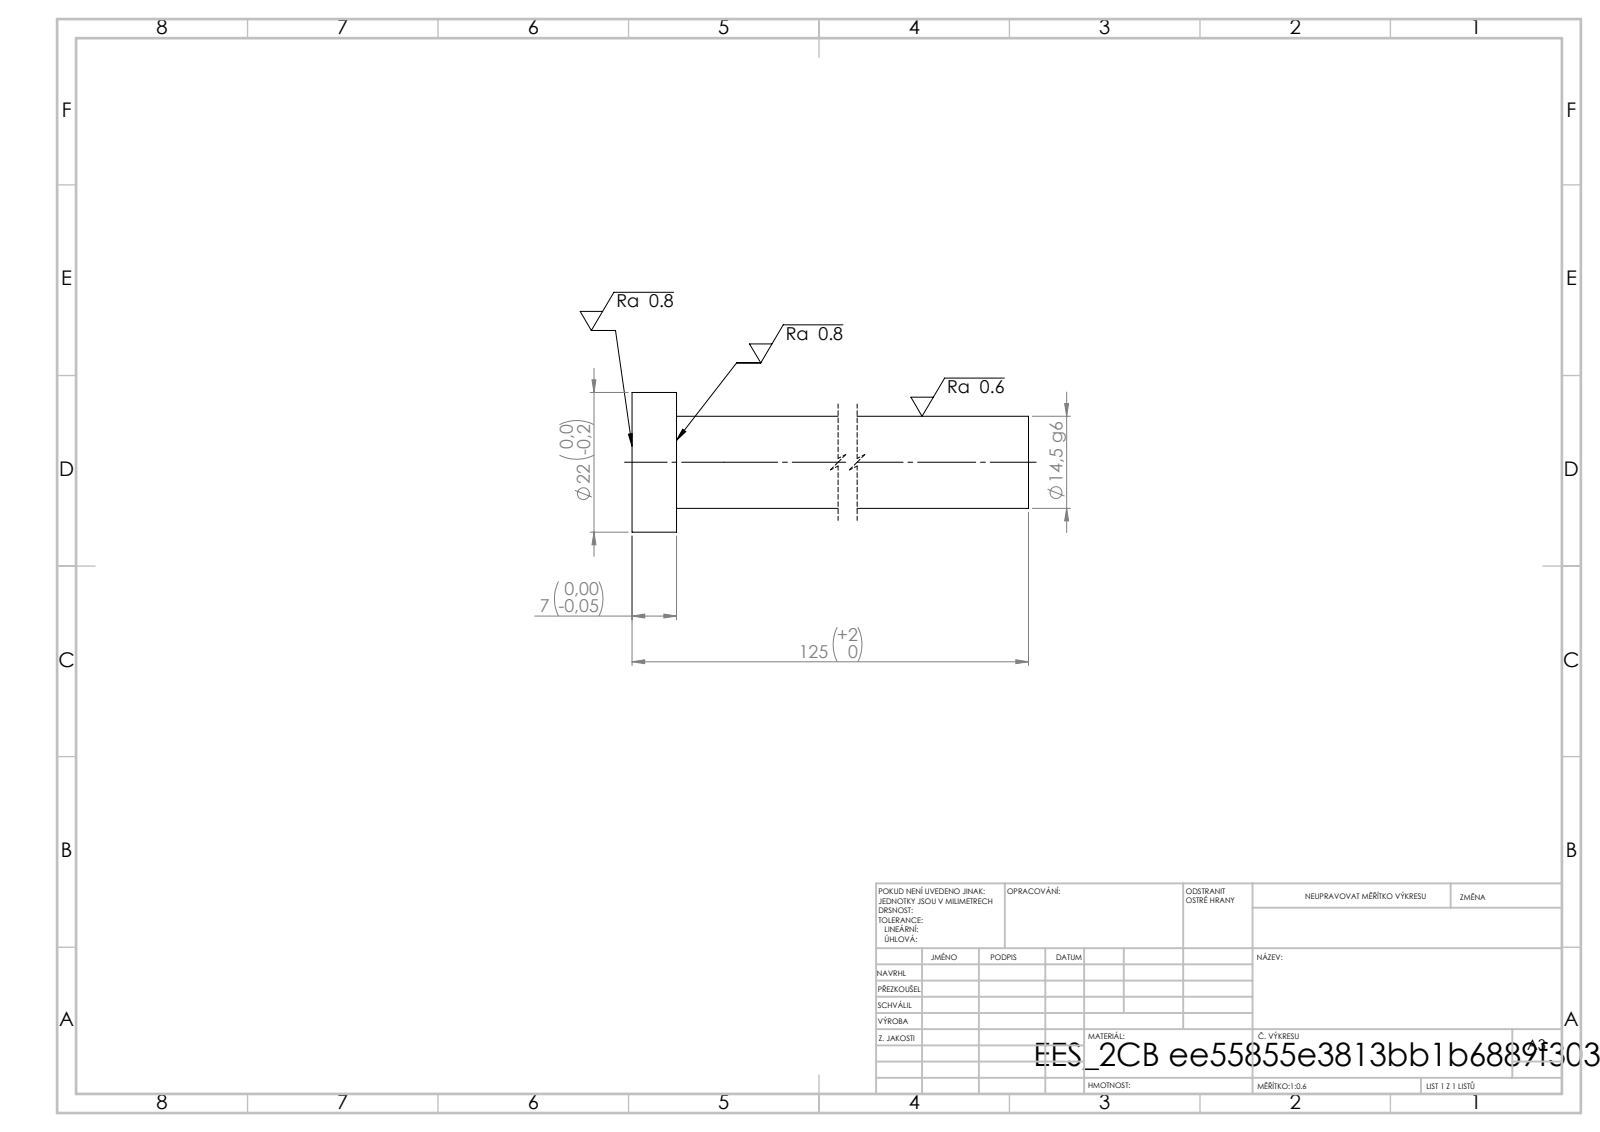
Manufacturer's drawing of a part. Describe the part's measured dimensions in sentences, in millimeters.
Its 3-D file was written by "SolidWorks 2019 (CONFIG_CONTROL_DESIGN)". It is 1 solid with 7 faces: 3 planar, 4 cylindrical and 0 other. Overall it measures 125 by 22 by 22 millimeters. Its volume is 22 146 cubic millimeters and its surface area 6 619 square millimeters. Round bosses or shafts: 1 of diameter 22, 1 of diameter 14.5. The main face-to-face distances are 7, 125, 118.
